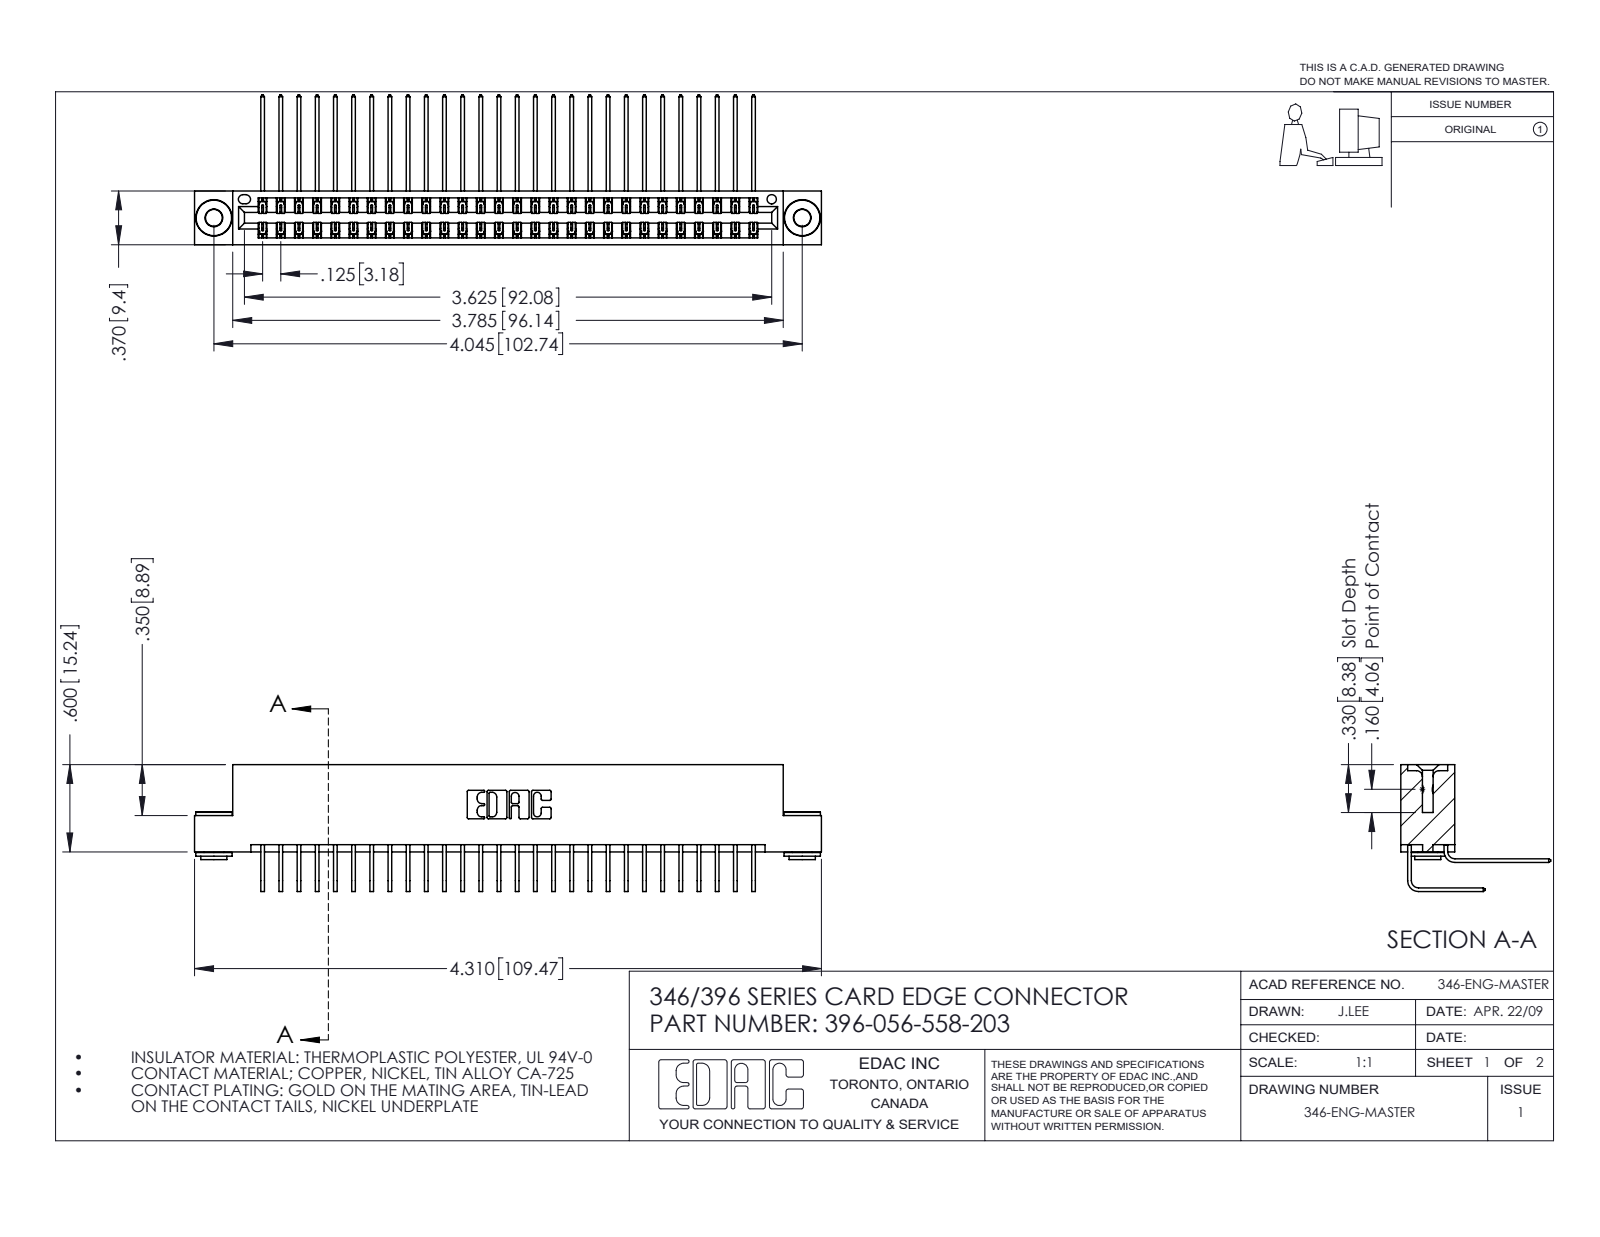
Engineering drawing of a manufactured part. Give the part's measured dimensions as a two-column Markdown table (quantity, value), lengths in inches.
| quantity | value |
| --- | --- |
| part name | 345-250-002_345-250-002-102; 346 Part_Flush Mounting Lugs - 0.156 Dia-TH; 345-292-001_558 559 Tail - 1; 345-292-001_558 Tail - 2 (+1 more) |
| STEP written by | SolidWorks 2016 (CONFIG_CONTROL_DESIGN) |
| units | inches |
| bodies | 59 solids, 3184 faces (2158 planar, 1018 cylindrical, 8 other) |
| overall size | 4.31 × 1.03 × 0.873 |
| volume | 0.666 in³ |
| surface area | 25.64 in² |
| round holes (diameter × count) | 0.116 × 2, 0.156 × 2, 0.064 × 1 |
| round bosses / shafts (diameter × count) | 0.25 × 2, 0.18 × 2, 0.136 × 2 |
| partial cylindrical surfaces (radius × count) | 0.006 × 84, 0.01 × 22, 0.007 × 6, 0.031 × 6, 0.026 × 3, 0.014 × 2, 0.022 × 2, 0.024 × 2 |
| main face-to-face distances | 0.322, 0.048, 0.025, 0.25, 0.37, 0.298, 0.072, 0.275, 0.148, 0.222 |
| hole center spacings | 0.246, 3.837, 4.045 |
